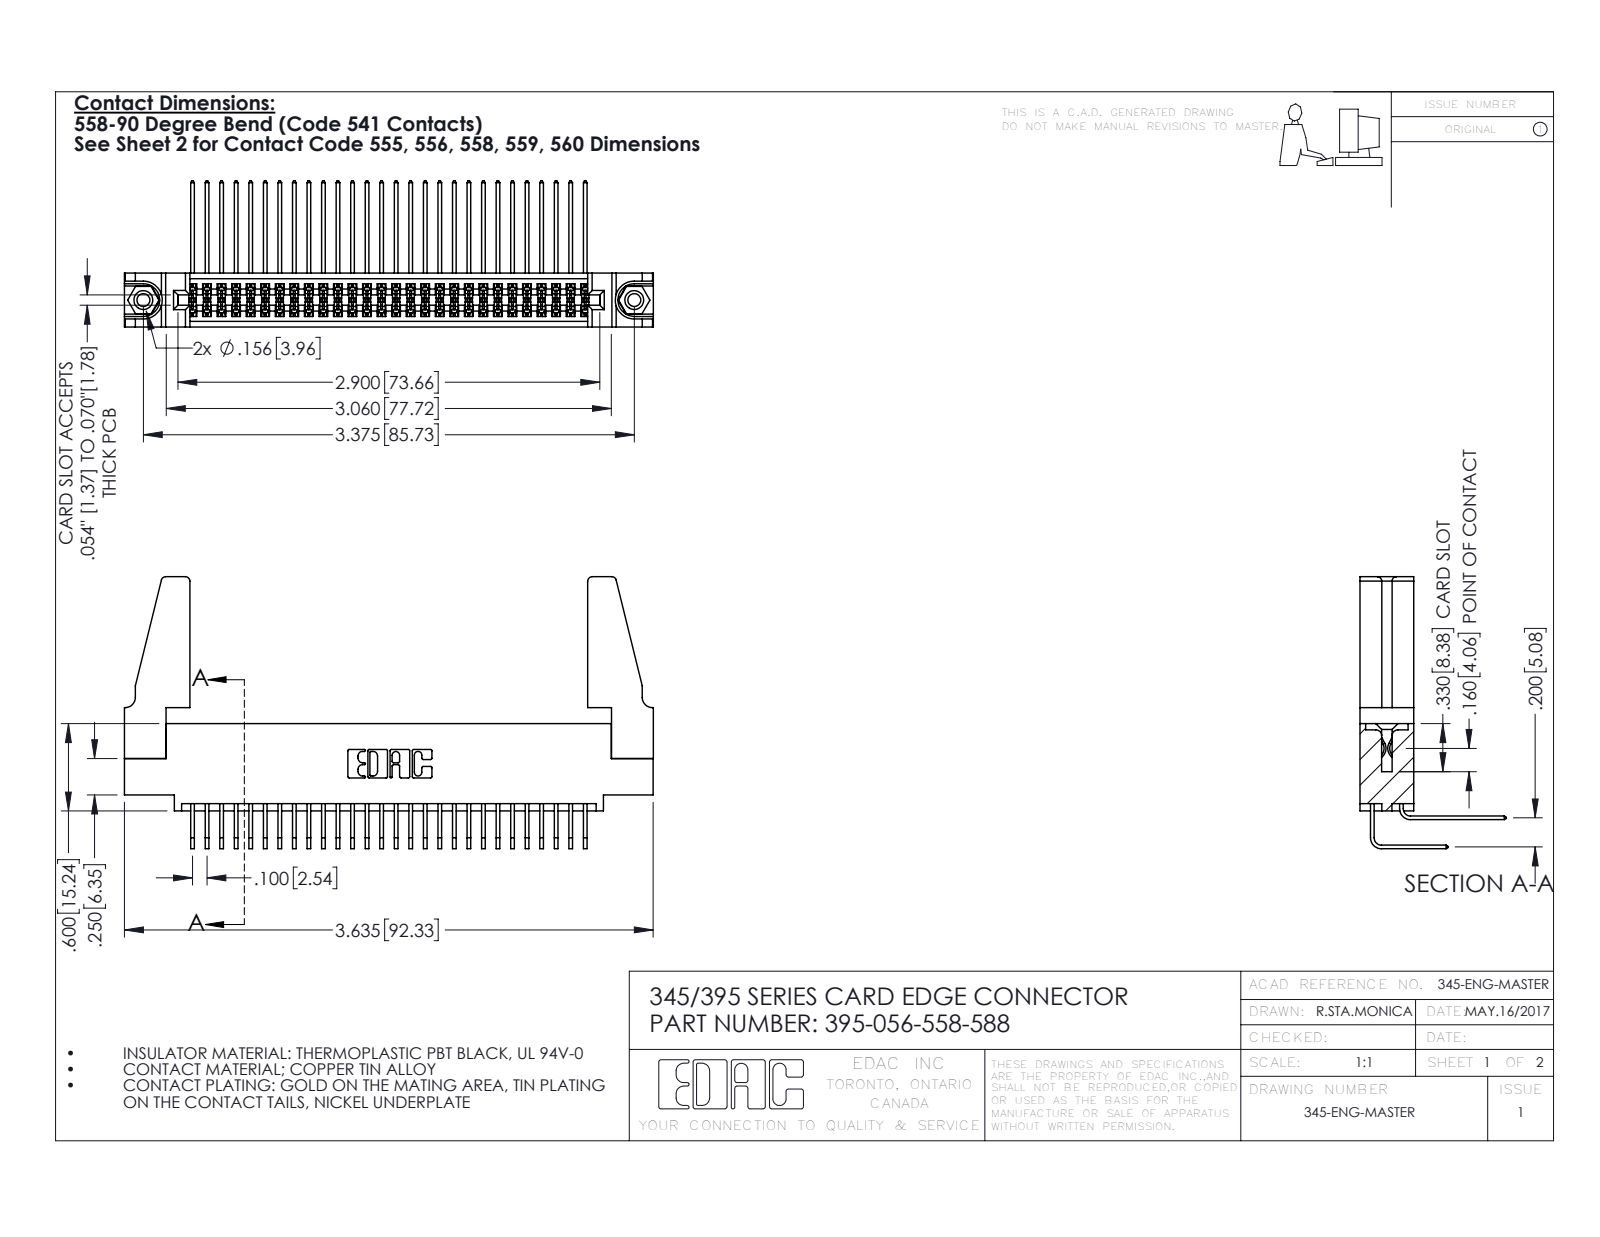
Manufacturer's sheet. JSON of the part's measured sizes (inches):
{"part_name": "395-056-558-588; 345-250-001_345-250-001-102; 345 Part_0.110 Offset - 0.156 Dia-TH; 345-292-001_558 559 Tail - 1 (+2 more)", "step_written_by": "SolidWorks 2016 (CONFIG_CONTROL_DESIGN)", "units": "inches", "bodies": {"solids": 61, "faces": 3166, "planar": 2116, "cylindrical": 1034, "other": 16}, "overall_size": [3.636, 1.869, 1.005], "volume_in3": 0.753, "surface_area_in2": 27.75, "round_holes": [[0.089, 2], [0.125, 2], [0.156, 2], [0.064, 1]], "round_bosses_or_shafts": [[0.155, 2]], "partial_cylinders_radius": [[0.006, 85], [0.01, 22], [0.03, 8], [0.007, 6], [0.031, 6], [0.026, 3], [0.014, 2], [0.019, 2]], "face_to_face_distances": [0.072, 0.298, 0.37, 0.2, 0.098, 0.272, 0.025, 0.225, 0.025, 0.175], "hole_center_spacings": [0.27, 3.14, 3.375]}
